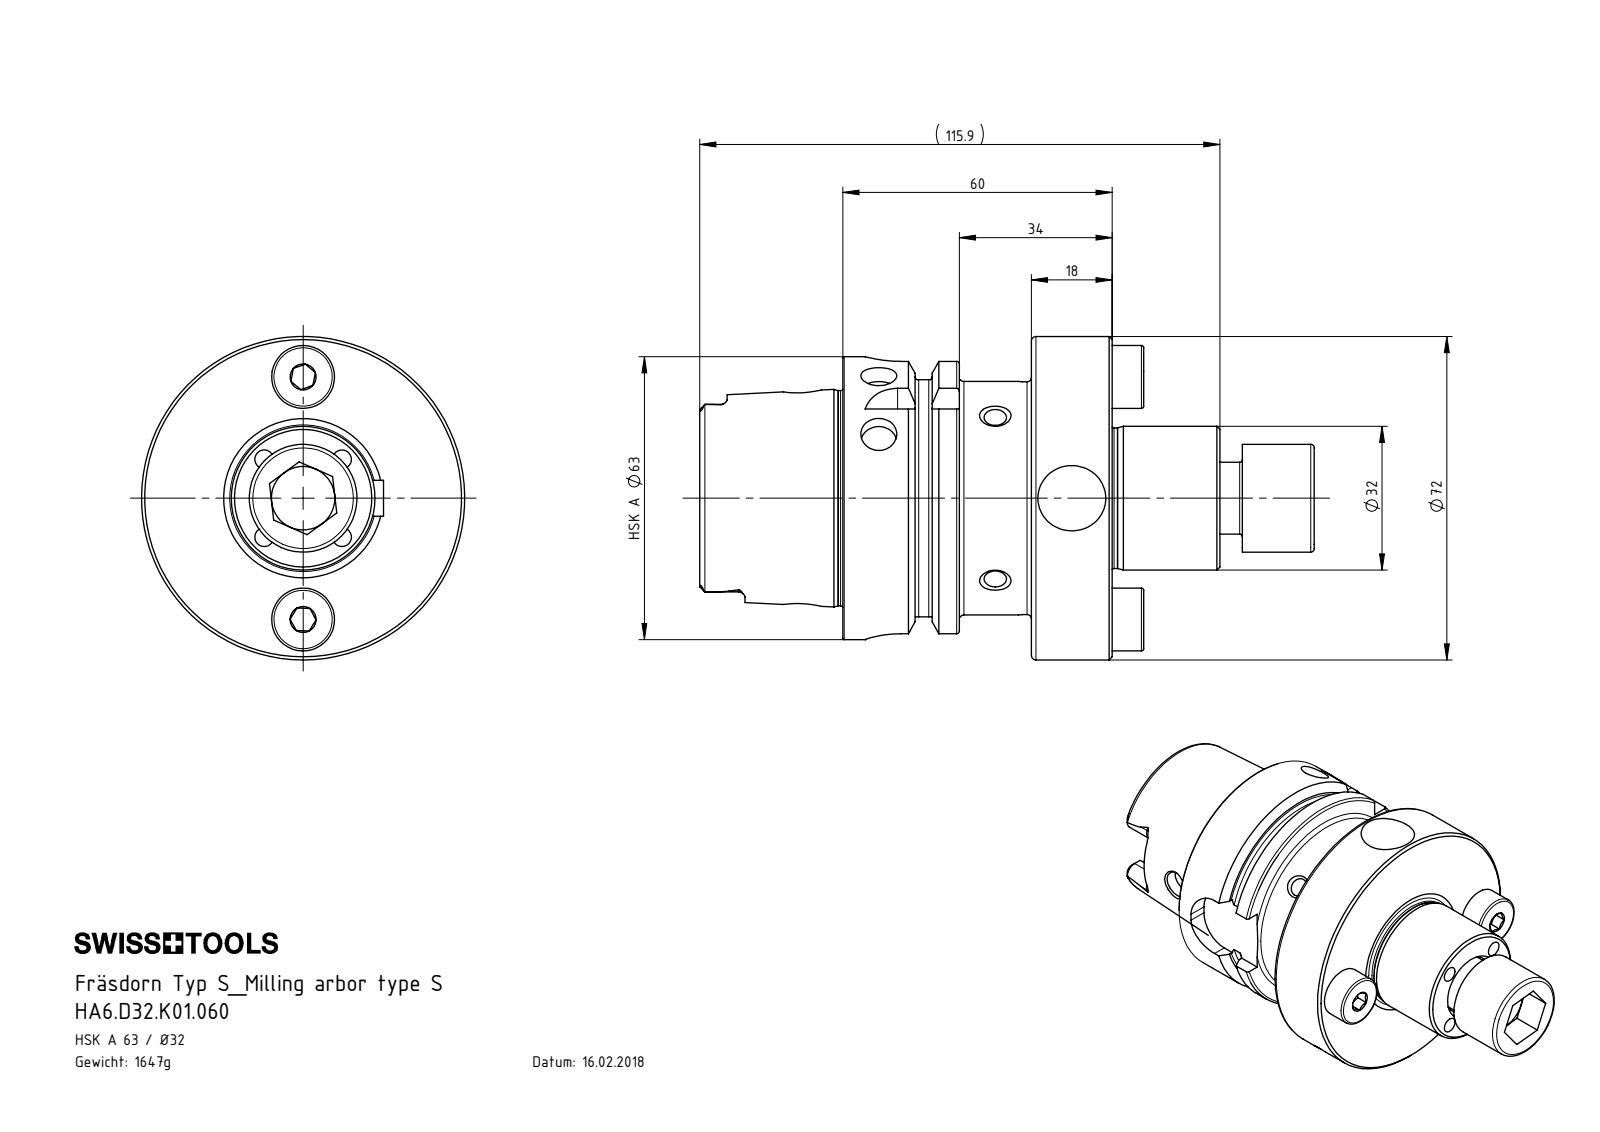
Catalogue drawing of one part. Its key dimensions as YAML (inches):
part_name: "HA6.D32.K01.060; D32-ER1.002.035_A; DIN 6885 - 8x7x16; D32-ER2.001.022_B (+1 more)"
step_written_by: "SolidWorks 2017 (AUTOMOTIVE_DESIGN)"
units: inches
bodies: {solids: 5, faces: 268, planar: 96, cylindrical: 68, other: 104}
overall_size: [5.39, 2.835, 2.835]
volume: 12.87
surface_area: 73.24
round_holes:
  - {diameter: 0.197, count: 9}
  - {diameter: 0.315, count: 2}
  - {diameter: 0.472, count: 2}
  - {diameter: 0.295, count: 1}
  - {diameter: 0.331, count: 1}
  - {diameter: 0.394, count: 1}
  - {diameter: 0.551, count: 1}
  - {diameter: 0.669, count: 1}
  - {diameter: 0.748, count: 1}
  - {diameter: 1.339, count: 1}
  - {diameter: 1.575, count: 1}
round_bosses_or_shafts:
  - {diameter: 0.551, count: 2}
  - {diameter: 0.236, count: 2}
  - {diameter: 0.181, count: 2}
  - {diameter: 2.835, count: 1}
  - {diameter: 2.48, count: 1}
  - {diameter: 2.163, count: 1}
  - {diameter: 2.047, count: 1}
  - {diameter: 1.887, count: 1}
partial_cylinders:
  - {radius: 0.055, count: 6}
  - {radius: 0.113, count: 4}
  - {radius: 0.157, count: 4}
  - {radius: 0.315, count: 4}
face_to_face_distances: [0.709, 1.654, 2.362, 0.63, 1.022, 0.632, 1.341, 0.392, 1.262, 1.97]
hole_center_spacings: [0.482, 0.671, 0.798, 1.063, 1.445, 0.964, 2.126]
